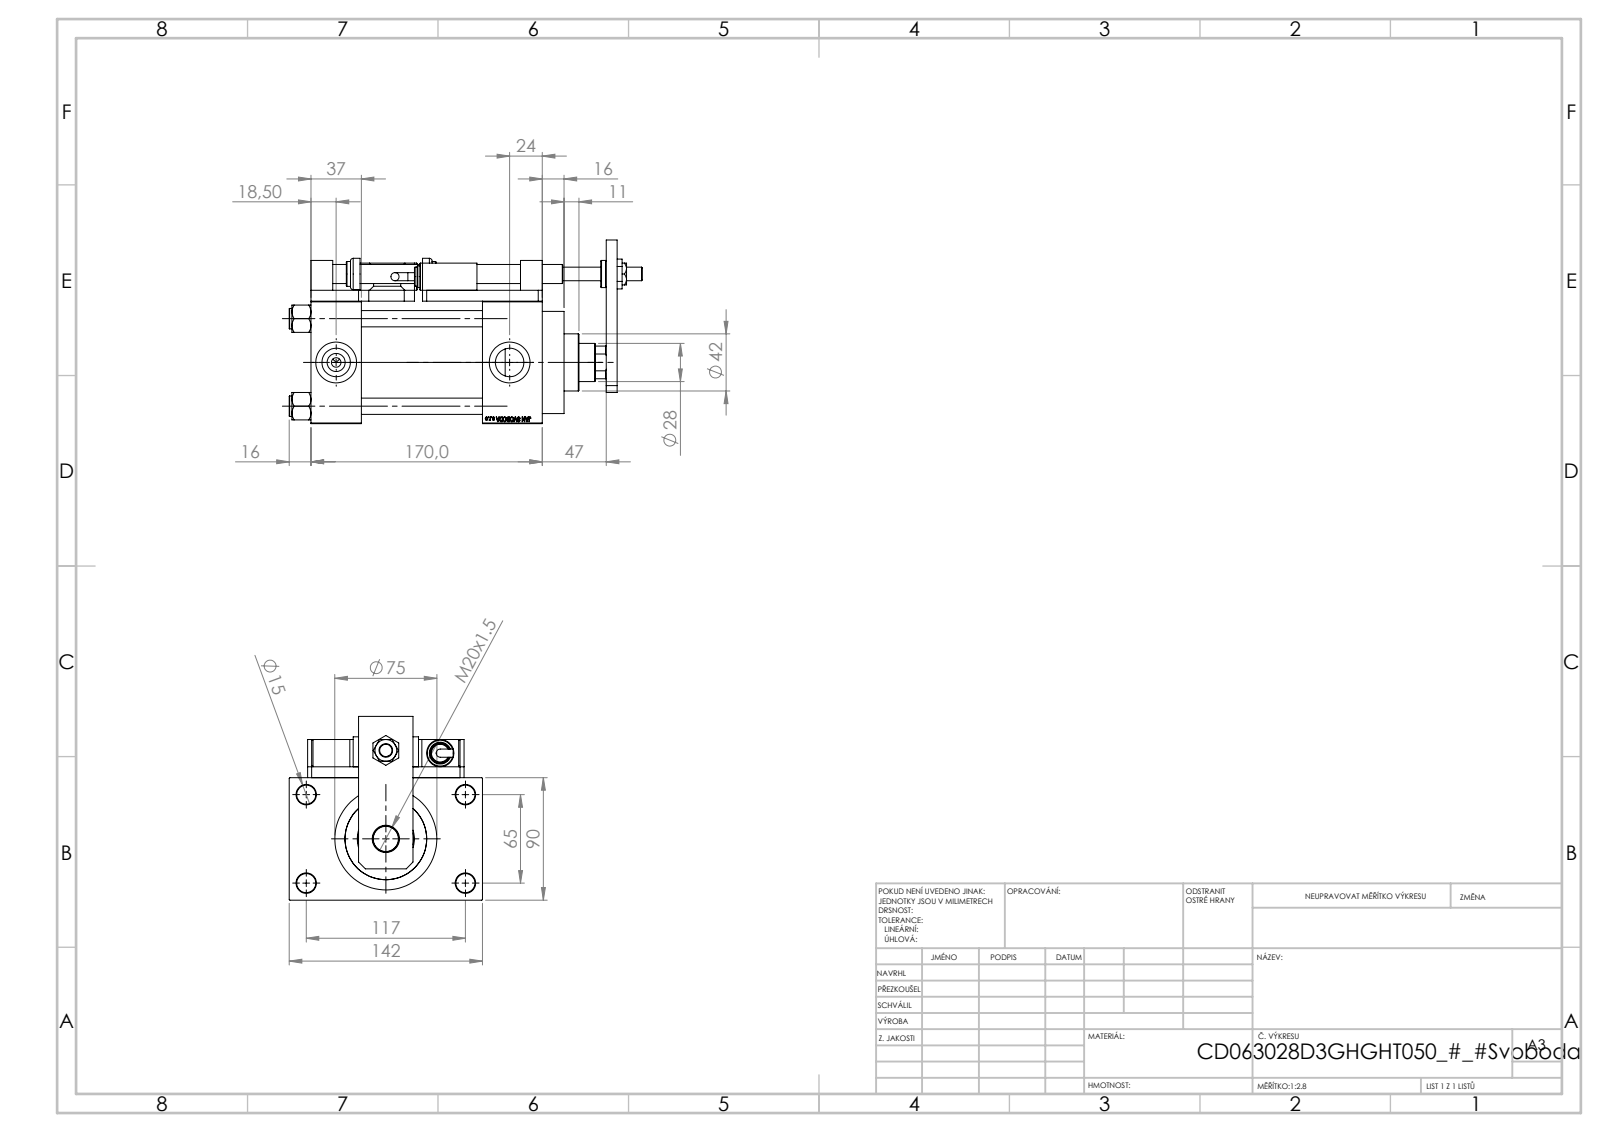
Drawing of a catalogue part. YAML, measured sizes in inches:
part_name: "V215CD_SWITCH_Q_SWITCH; V215CD_SWITCH_Q_MAGNET; V215CD_NUT_M5_D; V215CD_VC_A (+8 more)"
step_written_by: "SolidWorks 2019 (CONFIG_CONTROL_DESIGN)"
units: inches
bodies: {solids: 26, faces: 1432, planar: 666, cylindrical: 167, other: 599}
overall_size: [10.217, 5.591, 5.315]
volume: 86.1
surface_area: 482.2
round_holes:
  - {diameter: 0.551, count: 5}
  - {diameter: 0.335, count: 4}
  - {diameter: 0.472, count: 4}
  - {diameter: 0.531, count: 4}
  - {diameter: 0.825, count: 4}
  - {diameter: 1.181, count: 4}
  - {diameter: 0.276, count: 3}
  - {diameter: 0.394, count: 1}
  - {diameter: 0.728, count: 1}
  - {diameter: 0.787, count: 1}
  - {diameter: 1.102, count: 1}
  - {diameter: 1.22, count: 1}
round_bosses_or_shafts:
  - {diameter: 0.591, count: 4}
  - {diameter: 0.787, count: 3}
  - {diameter: 0.63, count: 2}
  - {diameter: 0.551, count: 2}
  - {diameter: 0.236, count: 2}
  - {diameter: 2.953, count: 1}
  - {diameter: 2.717, count: 1}
  - {diameter: 1.654, count: 1}
partial_cylinders:
  - {radius: 0.295, count: 4}
  - {radius: 0.531, count: 1}
face_to_face_distances: [0.315, 3.543, 1.732, 6.693, 1.457, 3.858, 5.236, 4.961, 3.504, 1.85]
hole_center_spacings: [2.635, 1.037, 1.79, 2.531, 2.748, 3.569, 4.383, 2.559]
